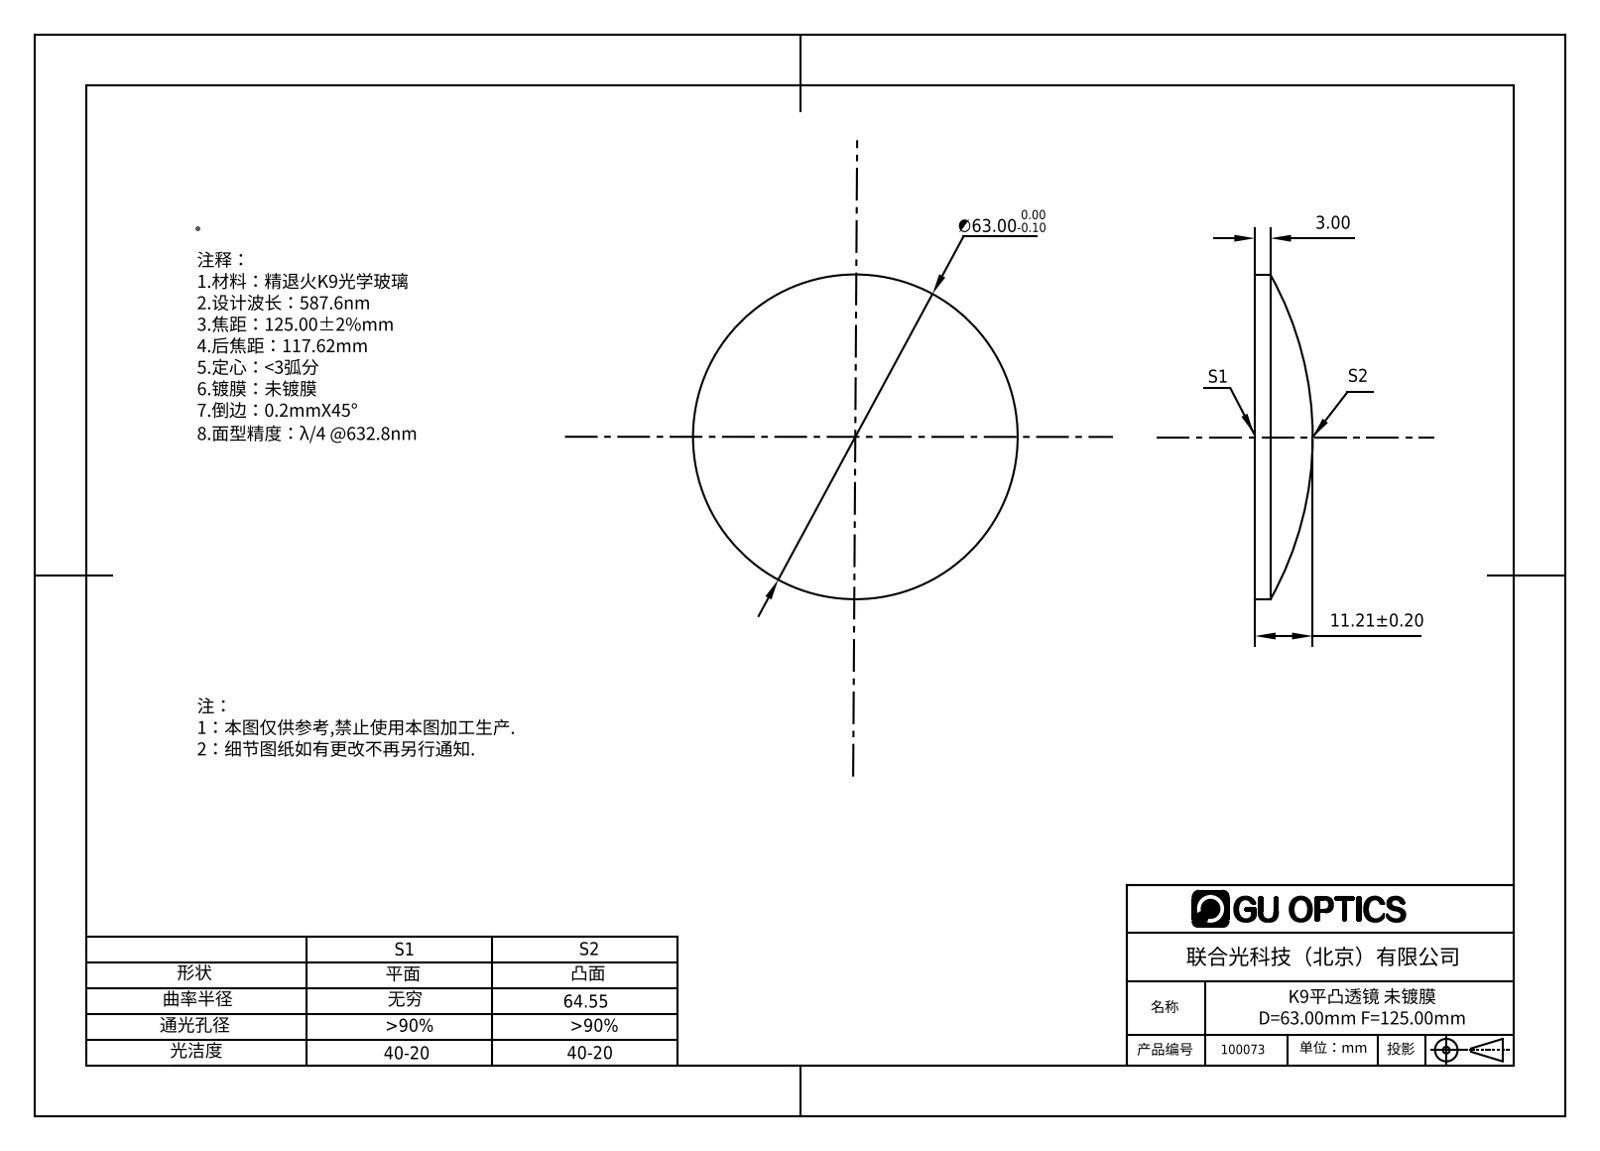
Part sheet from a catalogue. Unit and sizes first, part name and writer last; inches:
Units: inches
Overall size (bounding box): 2.48 × 2.48 × 0.441
Round bosses / shafts (diameter × count): ⌀2.48 ×1
Volume: 1.369 in³ · Surface area: 10.91 in²
Bodies: 1 solid, 5 faces (1 planar, 2 cylindrical, 2 other)
Part name (STEP PRODUCT): 100073
STEP written by: SolidWorks 2016 (AUTOMOTIVE_DESIGN)
